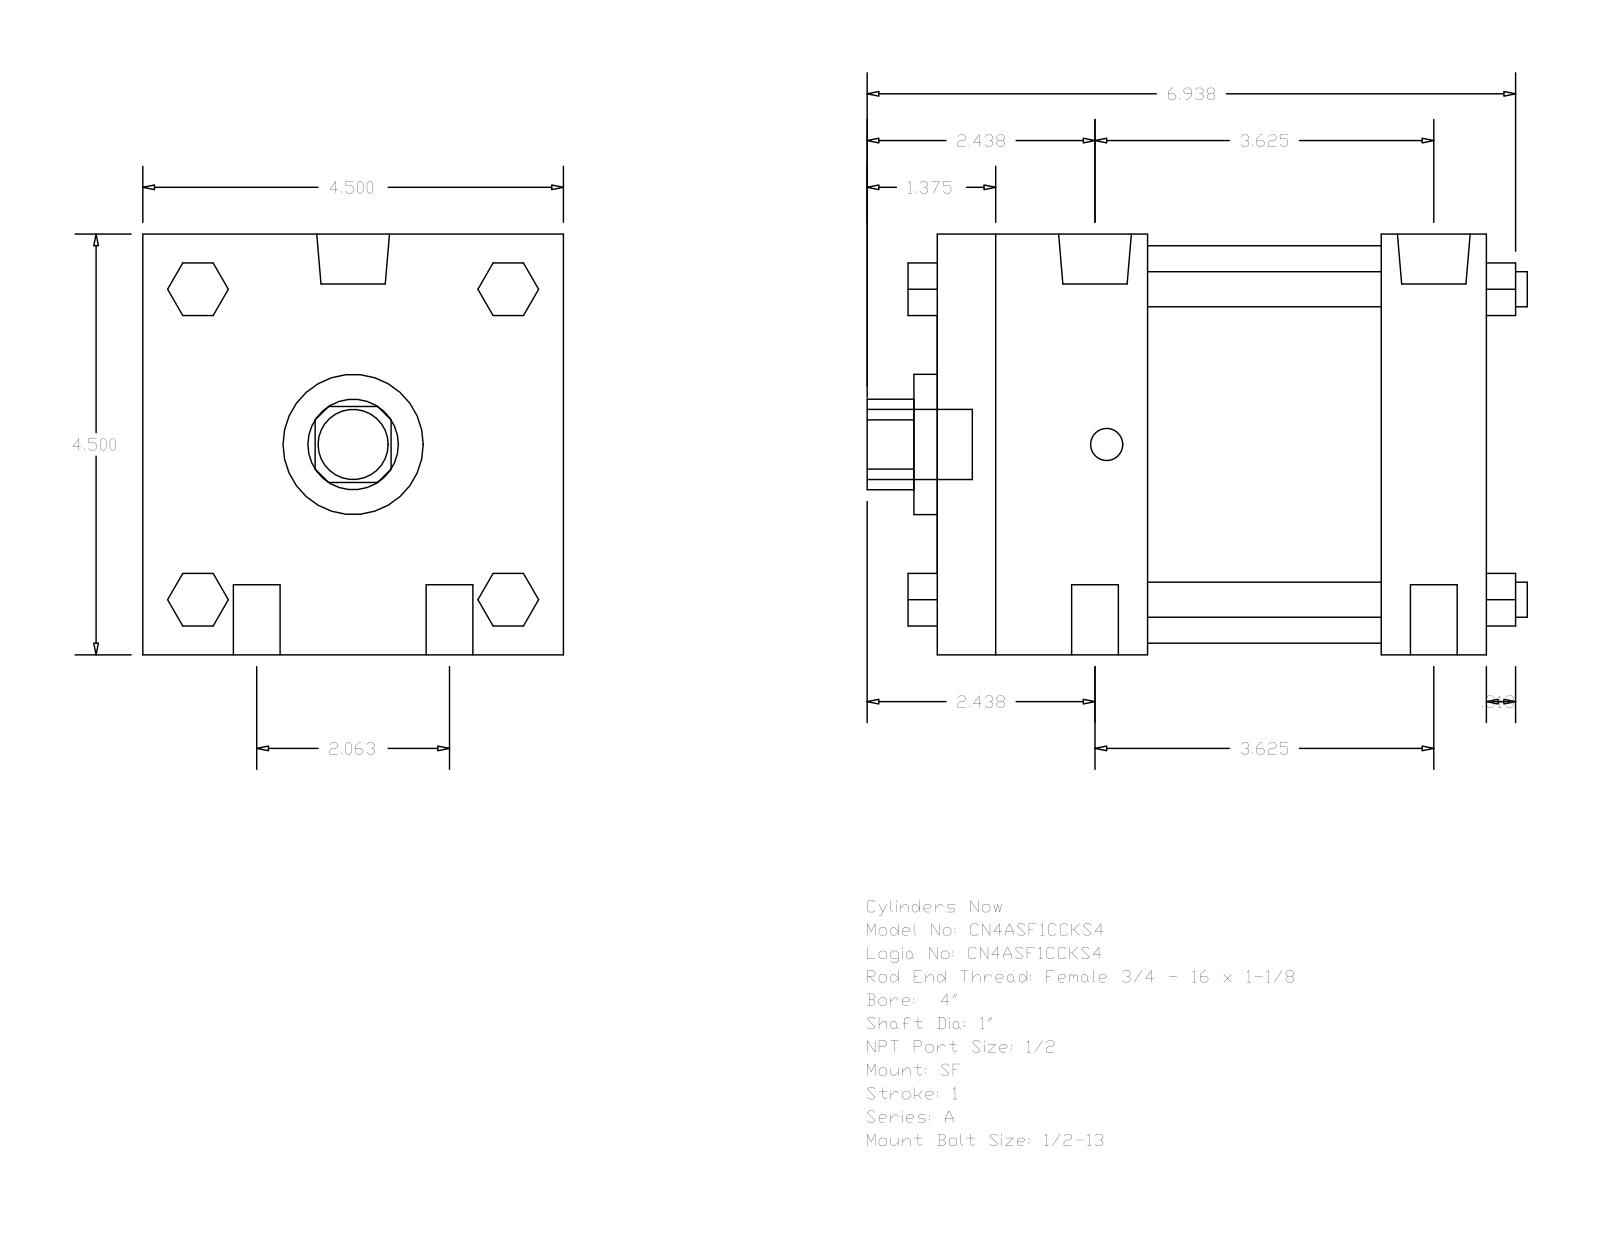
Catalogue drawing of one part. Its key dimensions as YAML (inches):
part_name: "A_SF__0400_1"
step_written_by: "GSSL Pune (CONFIG_CONTROL_DESIGN)"
units: inches
bodies: {solids: 0, faces: 124, planar: 94, cylindrical: 30, other: 0}
overall_size: [7.063, 4.5, 4.5]
round_holes:
  - {diameter: 1, count: 1}
  - {diameter: 1.5, count: 1}
  - {diameter: 4.25, count: 1}
round_bosses_or_shafts:
  - {diameter: 0.5, count: 4}
  - {diameter: 0.375, count: 4}
  - {diameter: 0.778, count: 2}
  - {diameter: 0.344, count: 2}
  - {diameter: 0.75, count: 1}
partial_cylinders:
  - {radius: 0.484, count: 1}
face_to_face_distances: [4.5, 5.875, 2.5, 4.75, 1.125, 2.25, 3.625, 0.563, 1.66, 2.875]
